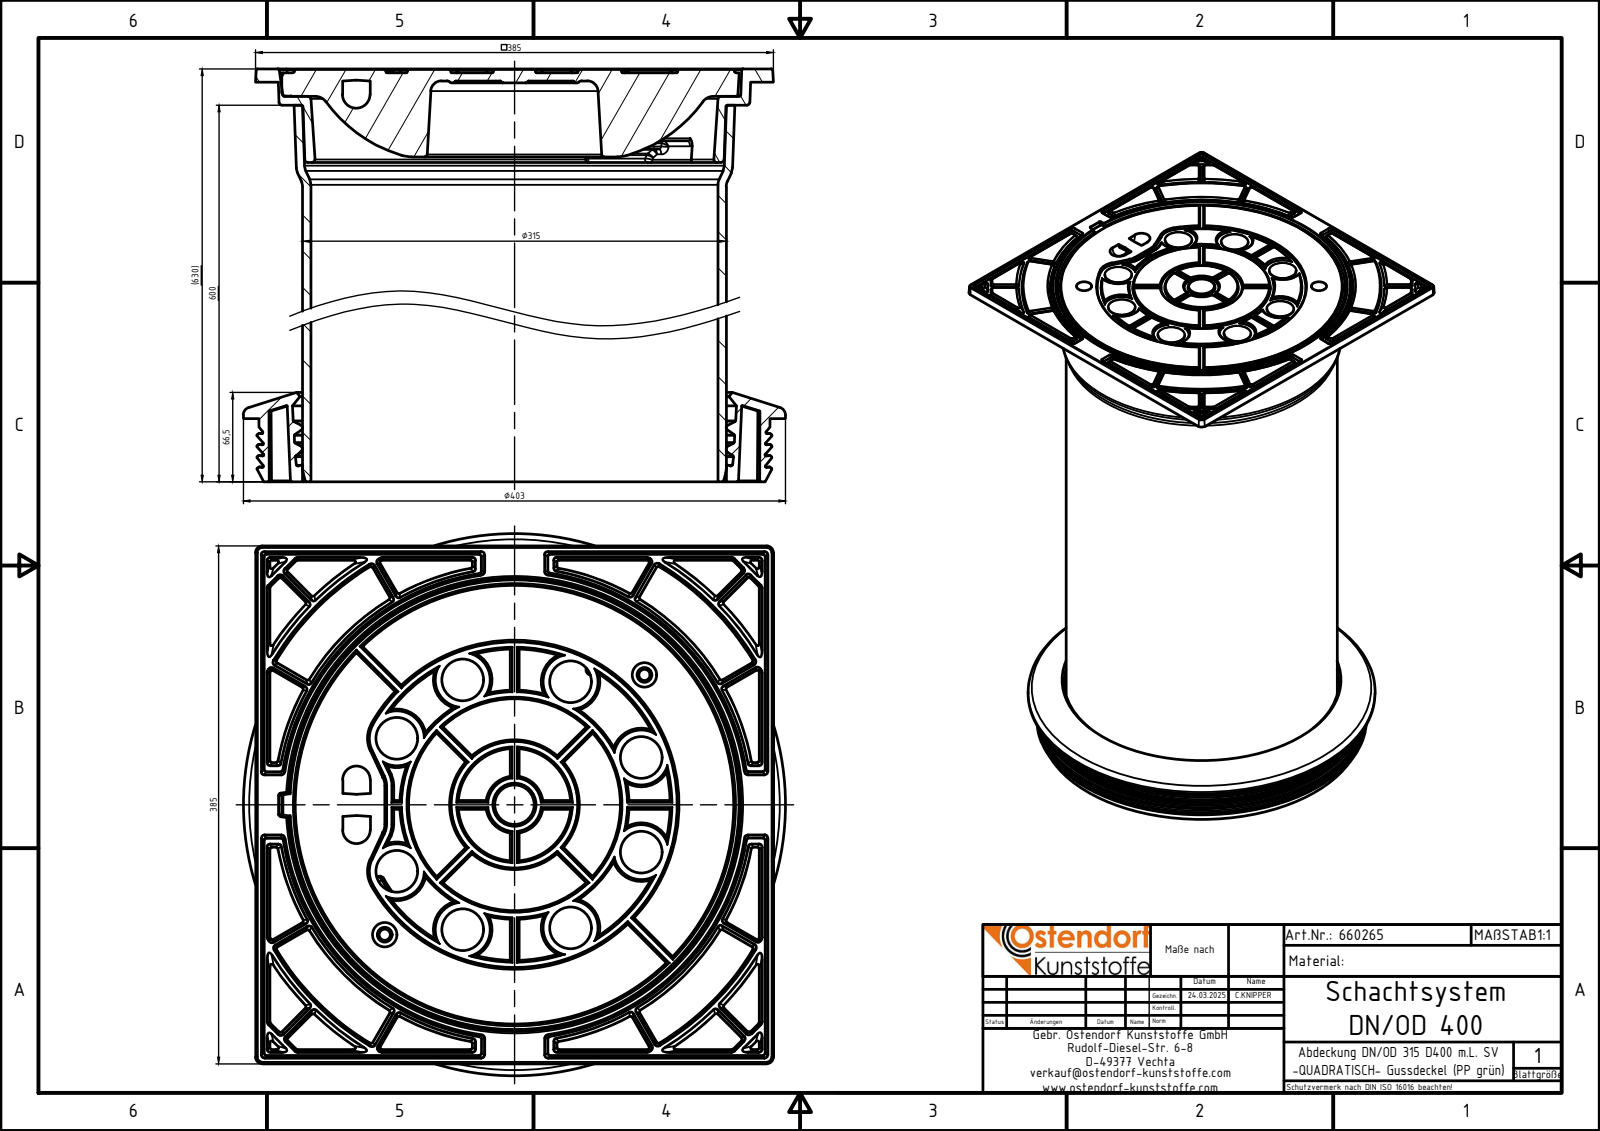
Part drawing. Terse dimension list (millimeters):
name: 660265z; 660300z; 660500_05.02.25z; 990050z (+1 more)
written by: Autodesk Inventor 2024 (AUTOMOTIVE_DESIGN)
unit: mm
bodies: 4 solids, 1838 faces (245 planar, 371 cylindrical, 1222 other)
size: 627 × 403 × 403
volume: 8 761 000 mm³; area: 2 157 000 mm²
holes: 8× ⌀31, 2× ⌀8.38, 2× ⌀11, 2× ⌀18, 1× ⌀302.6, 1× ⌀315
bosses: 1× ⌀403, 1× ⌀380
rounds: 208× R1, 48× R2.5, 18× R0.5, 8× R4, 4× R2, 1× R3
face distances: 9.5, 0.5, 10, 10.5, 20.5, 20, 6.5, 17, 26.5, 27
hole spacings: 100.5, 65.44, 76.92, 80.14, 100.49, 135.79, 137.08, 144.58
